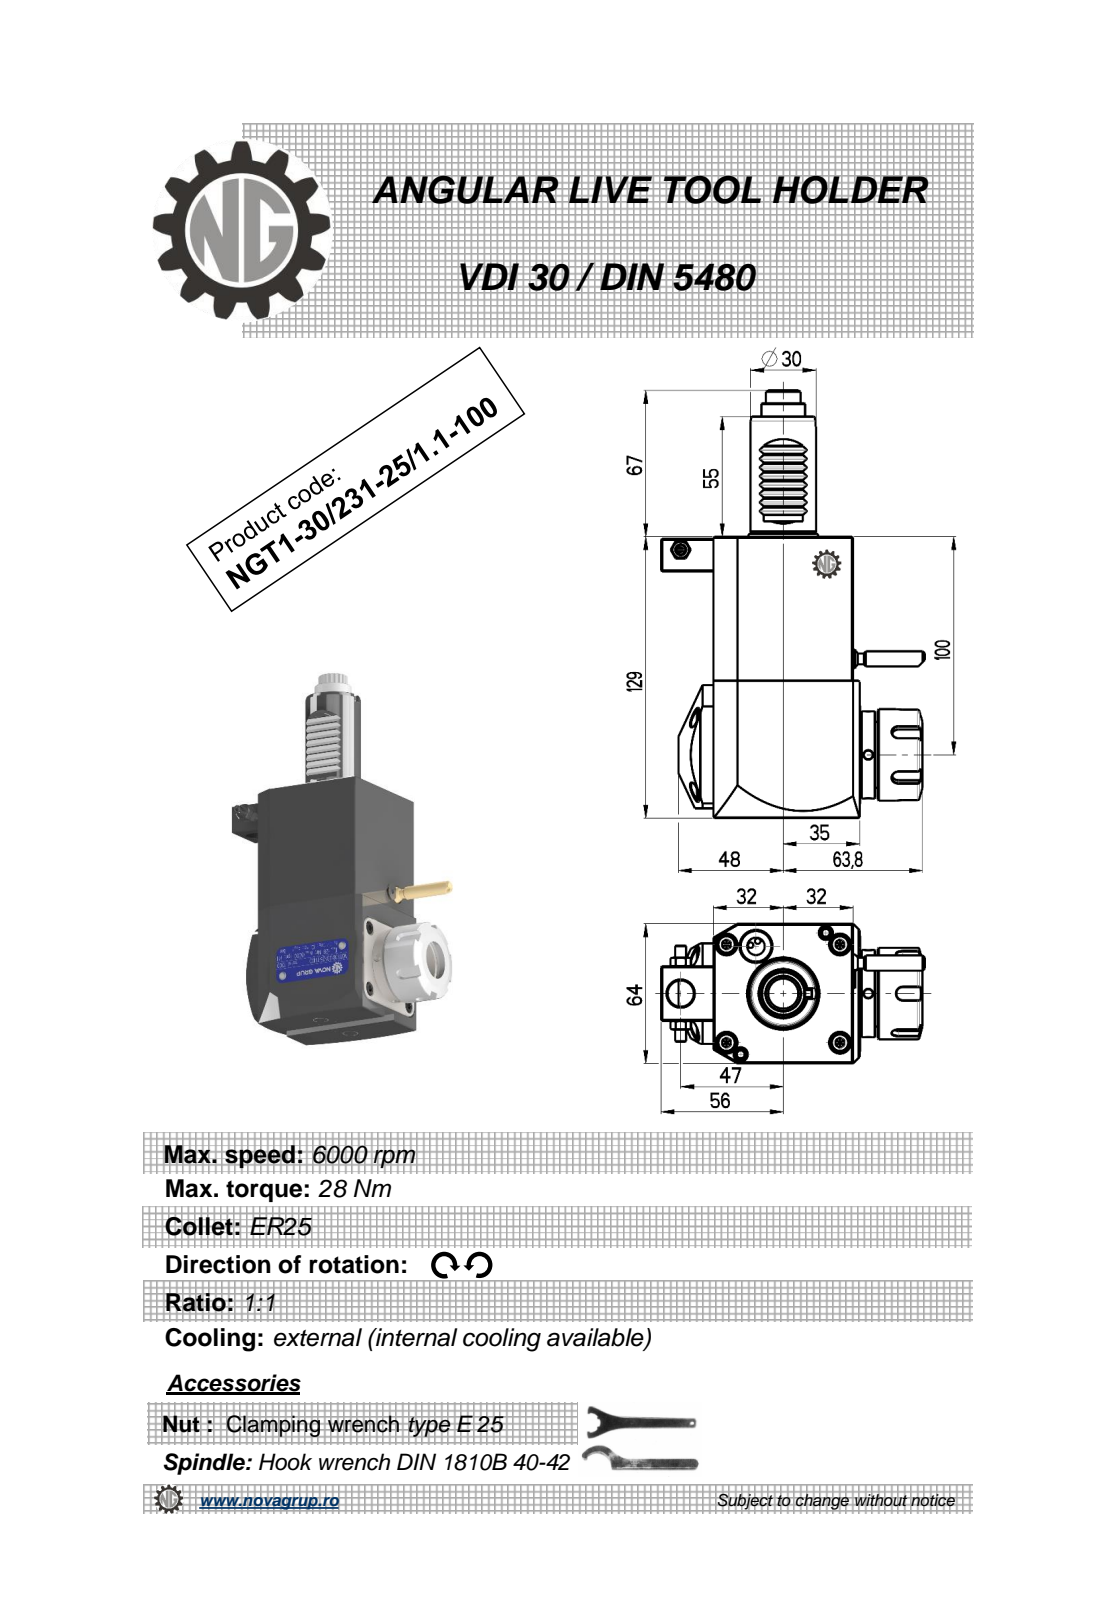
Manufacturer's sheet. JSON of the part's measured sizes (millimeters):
{"part_name": "NGT1_30_231_25_1_1_100", "step_written_by": "PRO/ENGINEER BY PARAMETRIC TECHNOLOGY CORPORATION, 2010280 (CONFIG_CONTROL_DESIGN)", "units": "millimeters", "bodies": {"solids": 1, "faces": 510, "planar": 188, "cylindrical": 161, "other": 161}, "overall_size": [196, 120.88, 65.6], "volume_mm3": 636542, "surface_area_mm2": 58374, "round_holes": [[4, 2], [2.5, 1], [3, 1], [4.2, 1], [9.5, 1], [12, 1], [20.3, 1]], "round_bosses_or_shafts": [[8.96, 2], [5, 2], [42, 1], [40, 1], [33, 1], [30, 1], [20, 1], [7, 1]], "partial_cylinders_radius": [[1.98, 36], [0.26, 12], [0.3, 8], [3, 5], [3.5, 4], [160, 2], [7.08, 1], [7.92, 1]], "face_to_face_distances": [64, 129, 67.2, 3.2, 67, 3, 0.5, 55, 16, 4], "hole_center_spacings": [46.17, 49.52, 85.95, 91.5, 127.37]}
